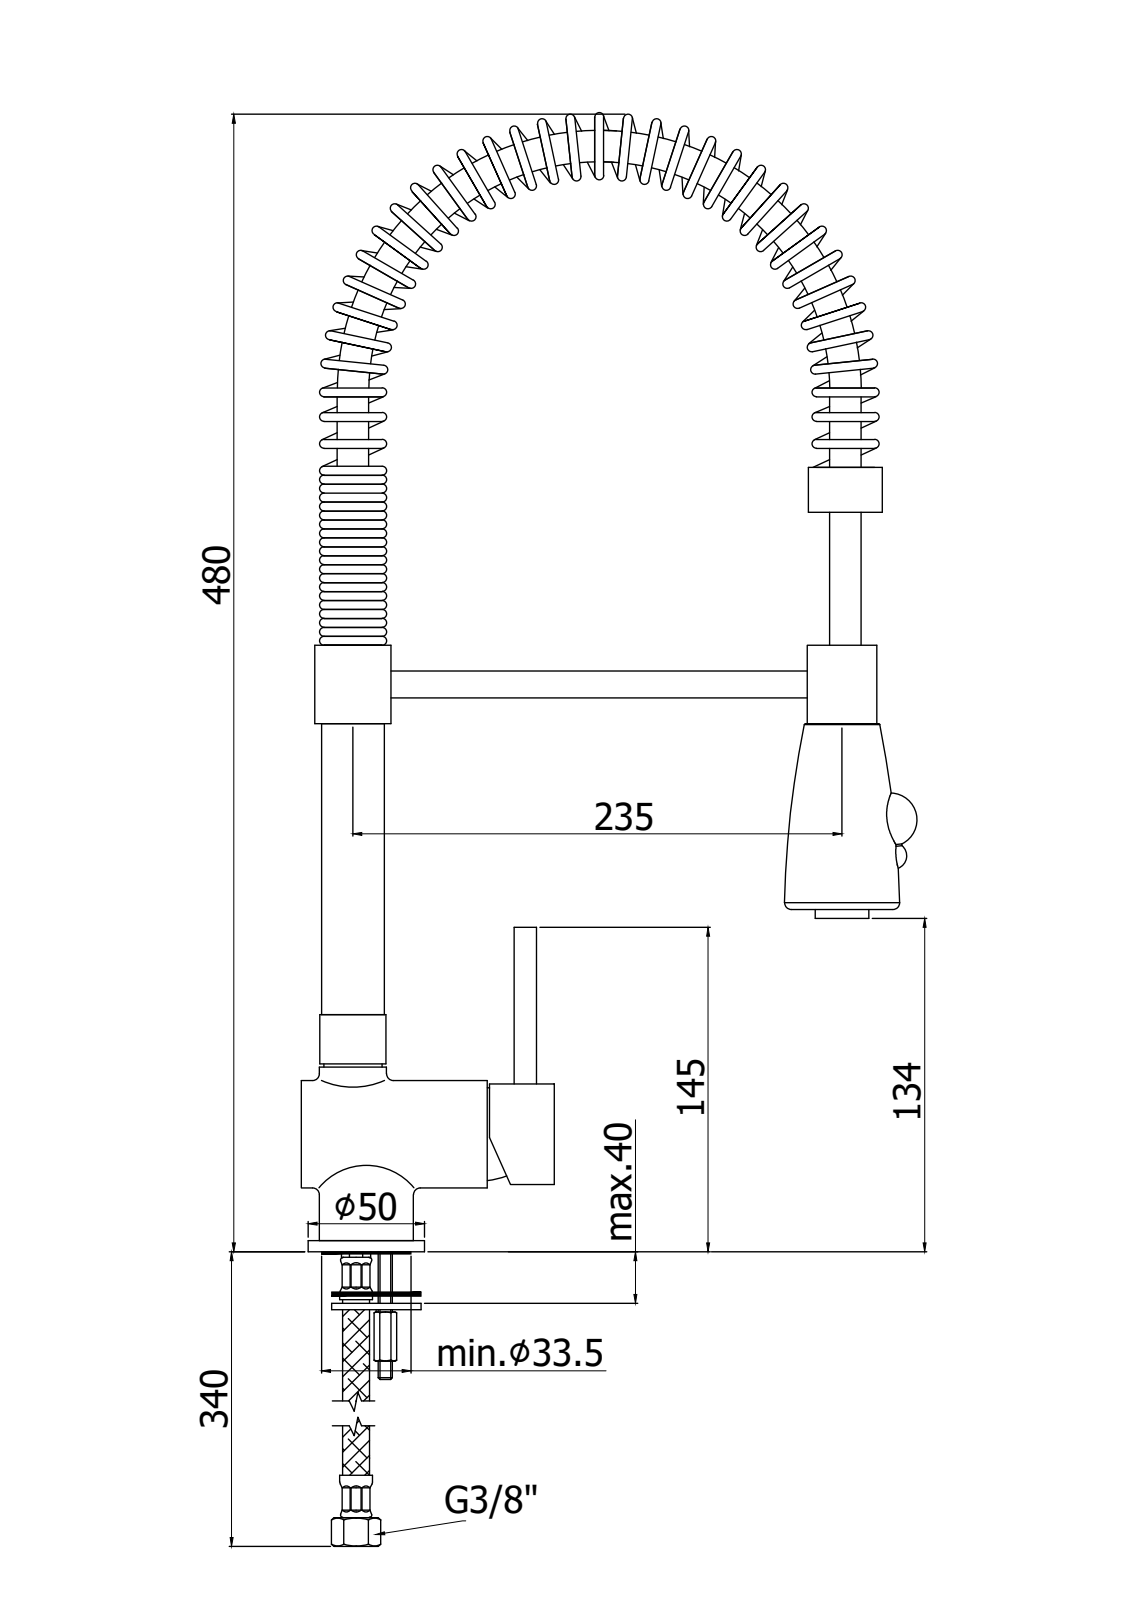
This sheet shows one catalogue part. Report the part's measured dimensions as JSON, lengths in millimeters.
{"part_name": "SK178CR", "step_written_by": "CREO PARAMETRIC BY PTC INC, 2020044 (CONFIG_CONTROL_DESIGN)", "units": "millimeters", "bodies": {"solids": 5, "faces": 271, "planar": 57, "cylindrical": 69, "other": 145}, "overall_size": [512.64, 348.09, 74.92], "volume_mm3": 578468, "surface_area_mm2": 148546, "round_holes": [[3, 1], [5.6, 1], [12, 1], [17, 1]], "round_bosses_or_shafts": [[13.5, 2], [49.5, 1], [45, 1], [44.5, 1], [43, 1], [38, 1], [35, 1], [31.5, 1]], "partial_cylinders_radius": [[0.5, 8], [2.25, 1], [2.75, 1], [17.5, 1]], "face_to_face_distances": [357, 372, 15, 226, 108.2, 131, 146, 94, 14.2, 8]}
